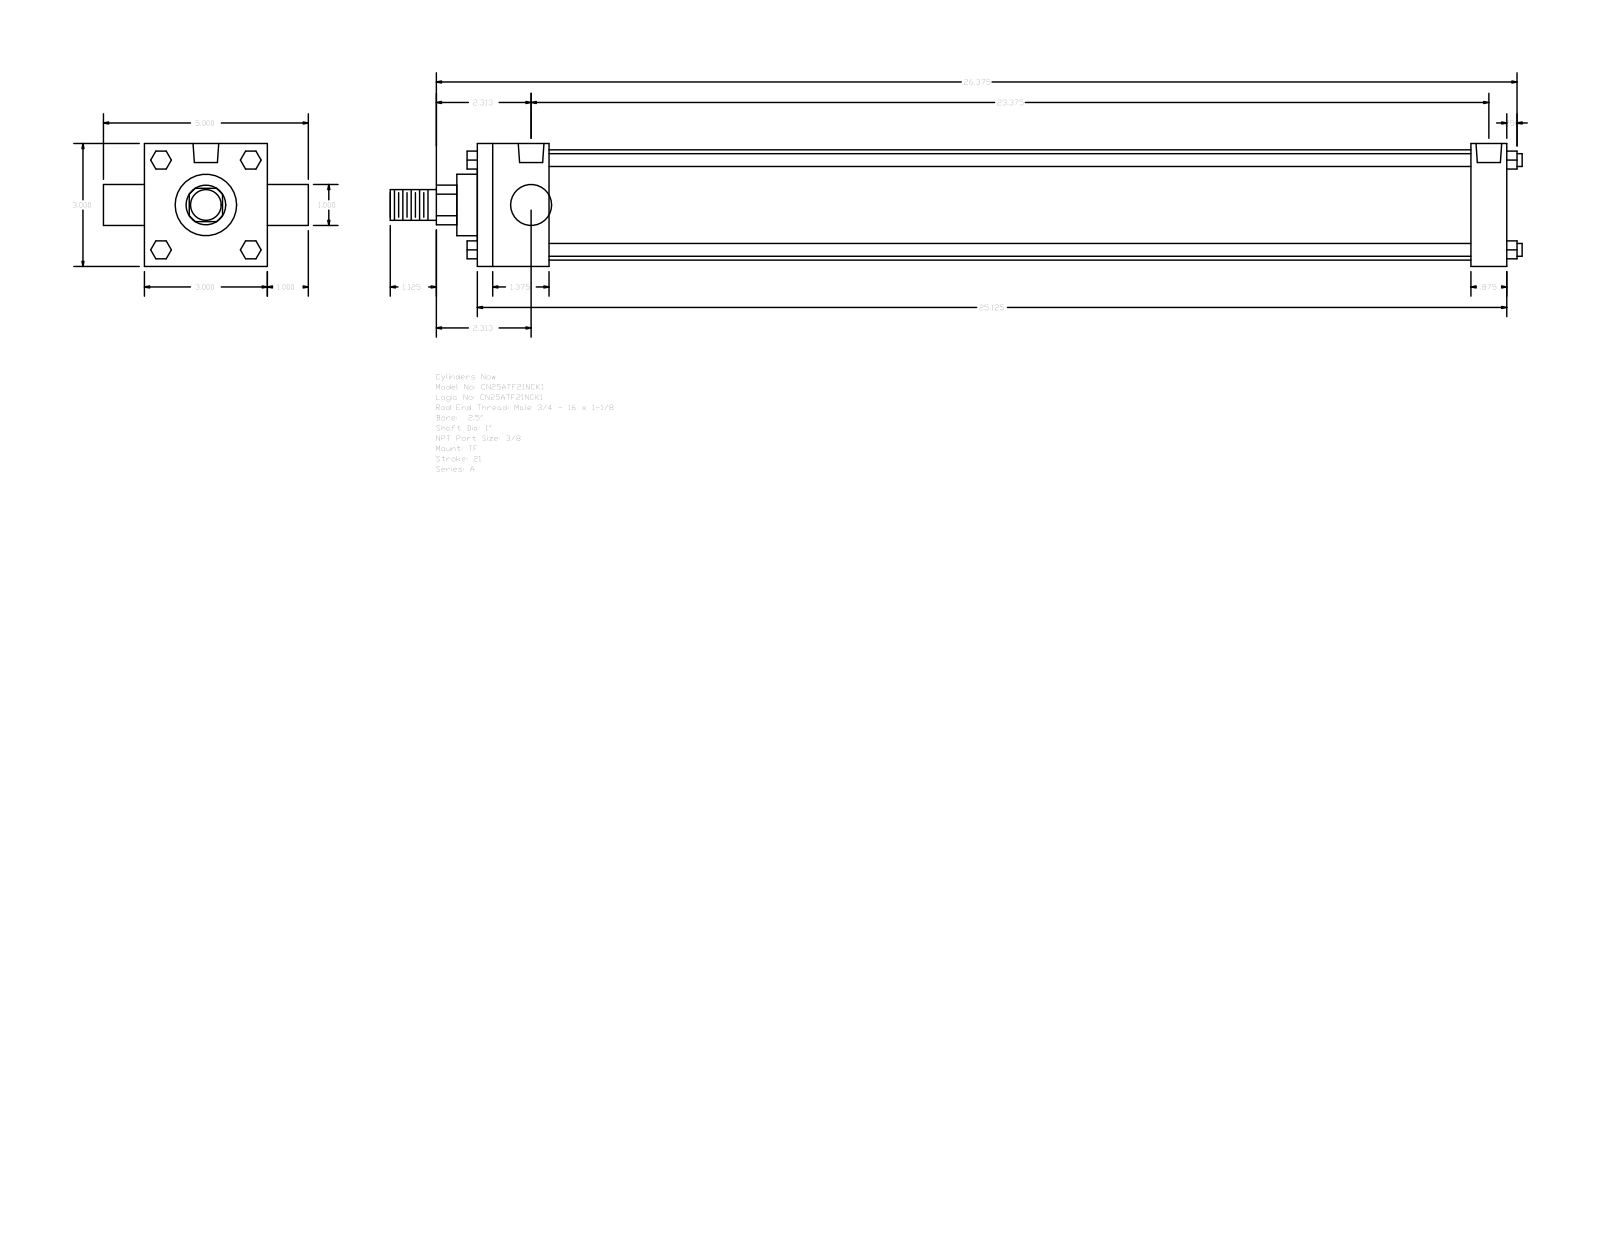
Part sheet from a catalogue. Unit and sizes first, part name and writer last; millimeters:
Units: millimetres
Overall size (bounding box): 701.67 × 127 × 76.2
Round holes (diameter × count): ⌀5.56 ×3, ⌀15.93 ×2
Round bosses / shafts (diameter × count): ⌀7.94 ×4, ⌀25.4 ×2, ⌀68.33 ×1, ⌀38.1 ×1, ⌀19.05 ×1
Partial cylindrical surfaces — rounded edges, fillets, slot ends (radius × count): R12.29 ×1
Main face-to-face distances: 76.2, 638.18, 44.45, 615.95, 571.5, 593.73, 22.23, 25.4, 101.6, 12.7
Hole centre spacings: 2.38, 596.1, 593.72, 598.48
Bodies: 0 solids, 120 faces (92 planar, 28 cylindrical, 0 other)
Part name (STEP PRODUCT): A_TF__0250_1
STEP written by: GSSL Pune (CONFIG_CONTROL_DESIGN)
